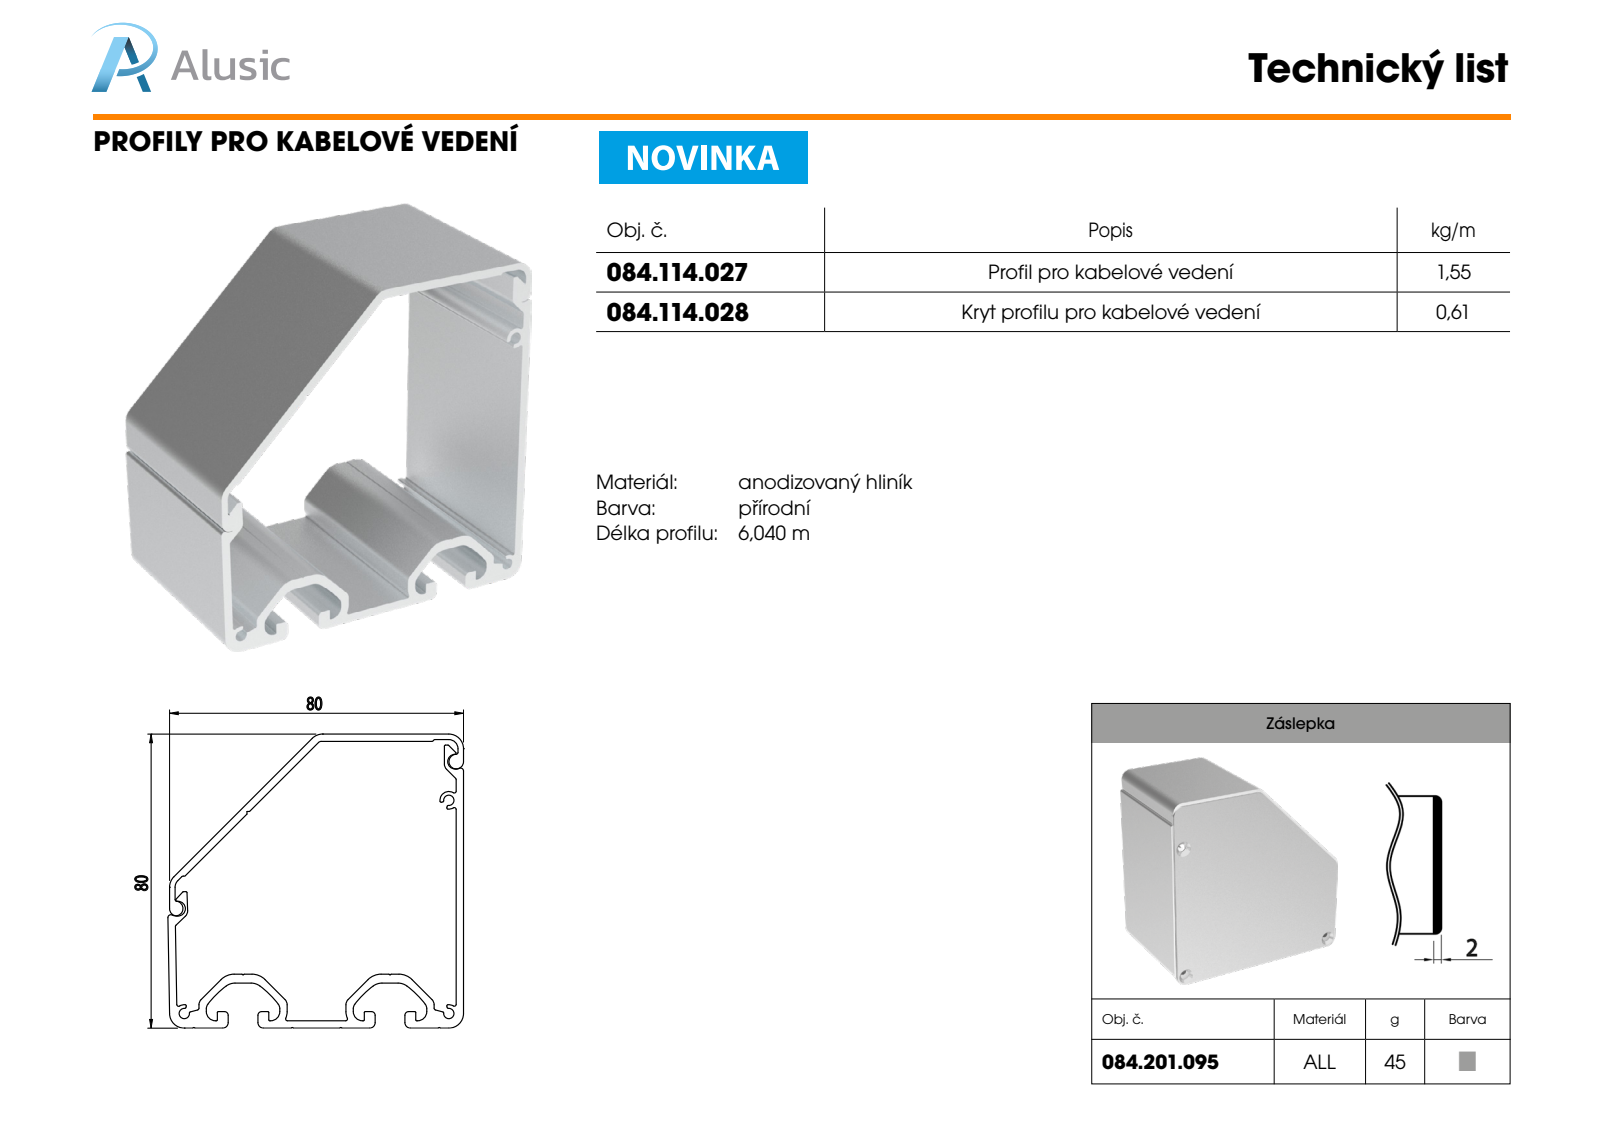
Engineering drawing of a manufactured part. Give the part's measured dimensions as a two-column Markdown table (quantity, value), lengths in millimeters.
| quantity | value |
| --- | --- |
| part name | 084.114.027 |
| STEP written by | SolidWorks 2018 (CONFIG_CONTROL_DESIGN) |
| units | millimeters |
| bodies | 1 solid, 182 faces (75 planar, 107 cylindrical, 0 other) |
| overall size | 100 × 80.45 × 77 |
| volume | 57 276 mm³ |
| surface area | 54 144 mm² |
| partial cylindrical surfaces (radius × count) | 0.3 × 16, 2 × 12, 0.5 × 10, 0.25 × 8, 0.12 × 6, 4 × 6, 1 × 4, 1.5 × 4 |
| main face-to-face distances | 2, 2.02, 28.28, 40, 12.25, 10.25, 14.68, 12.68, 2.43, 2.95 |
